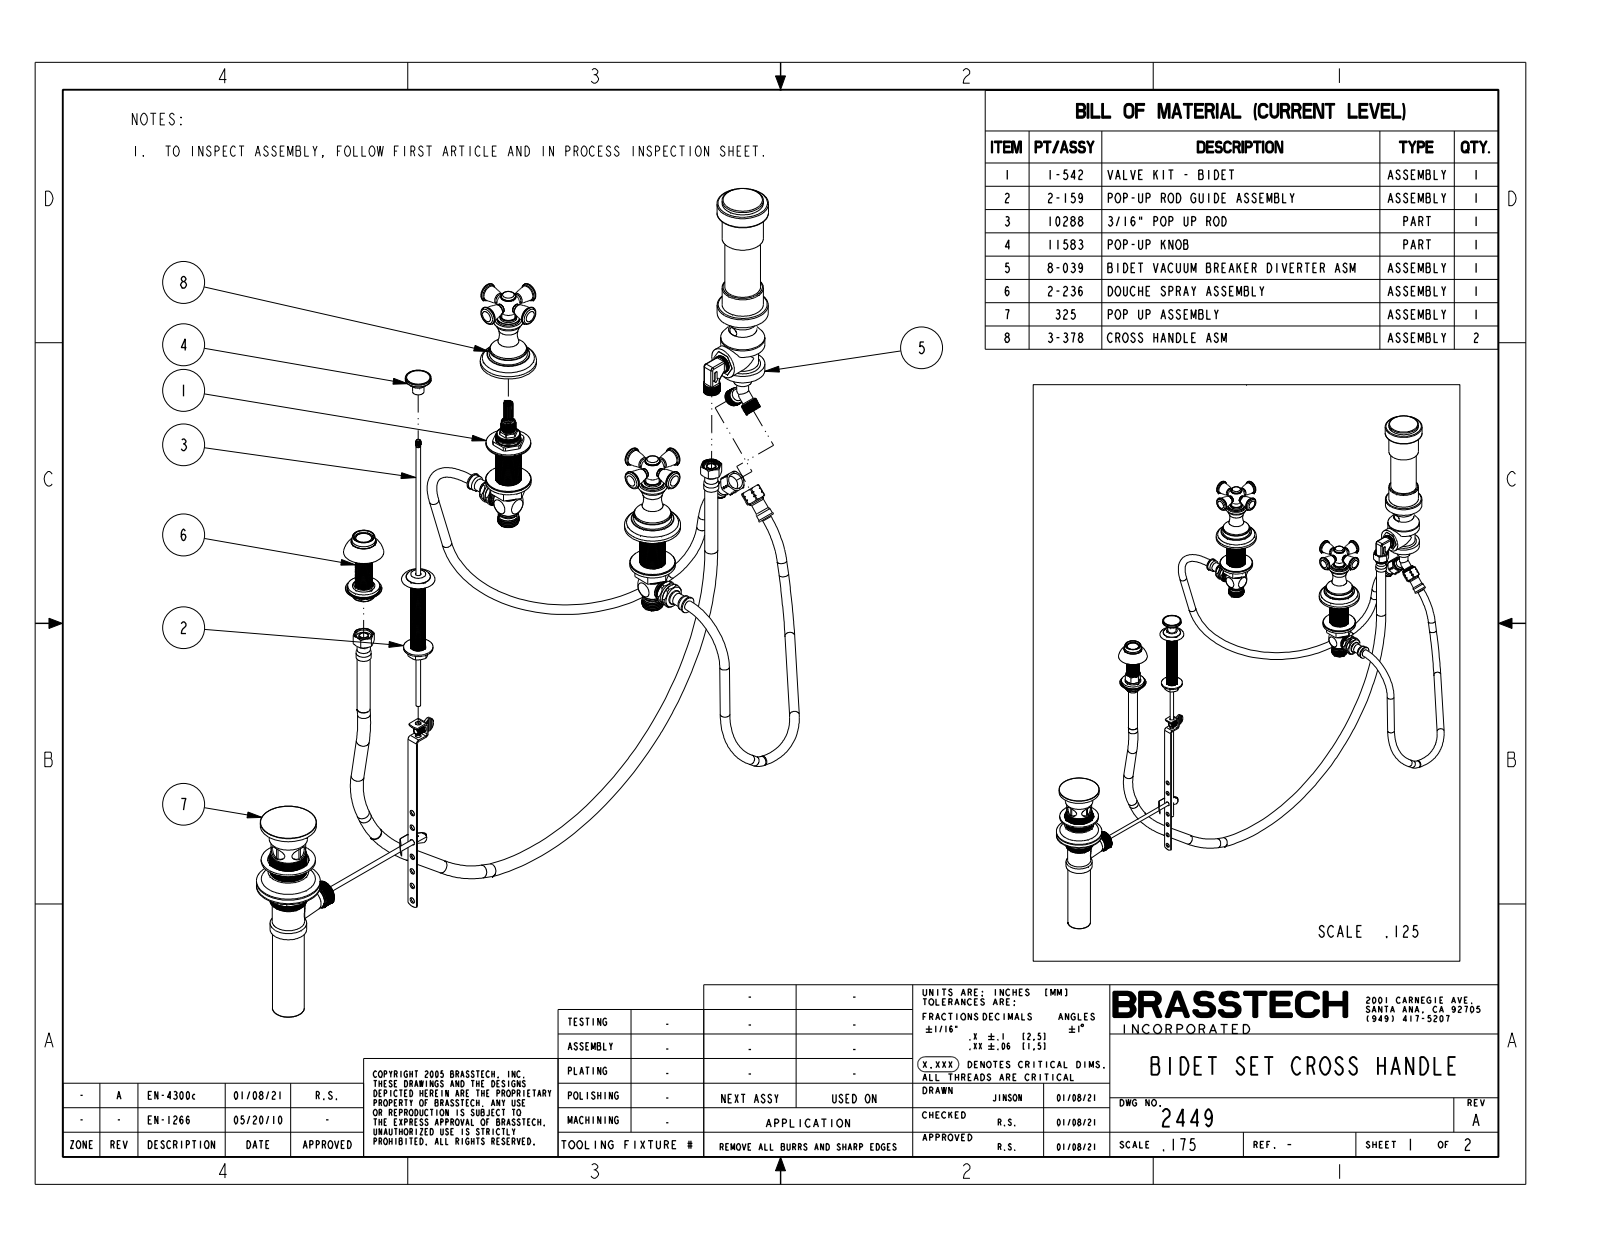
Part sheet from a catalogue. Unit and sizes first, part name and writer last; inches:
Units: inches
Overall size (bounding box): 22.798 × 10.528 × 5.445
Round holes (diameter × count): ⌀0.625 ×1, ⌀0.792 ×1, ⌀0.94 ×1
Round bosses / shafts (diameter × count): ⌀0.72 ×3, ⌀0.36 ×3, ⌀2.2 ×2, ⌀1.49 ×2, ⌀1.42 ×2, ⌀0.9 ×2, ⌀0.66 ×2, ⌀0.56 ×2
Partial cylindrical surfaces — rounded edges, fillets, slot ends (radius × count): R0.357 ×1
Main face-to-face distances: 5.445, 0.5, 5.295, 0.15, 4.795, 0.65, 0.42, 4.375, 4.875, 5.025
Volume: 20.4 in³ · Surface area: 98.76 in²
Bodies: 5 solids, 389 faces (67 planar, 94 cylindrical, 228 other)
Part name (STEP PRODUCT): 2449
STEP written by: CREO PARAMETRIC BY PTC INC, 2018400 (CONFIG_CONTROL_DESIGN)
